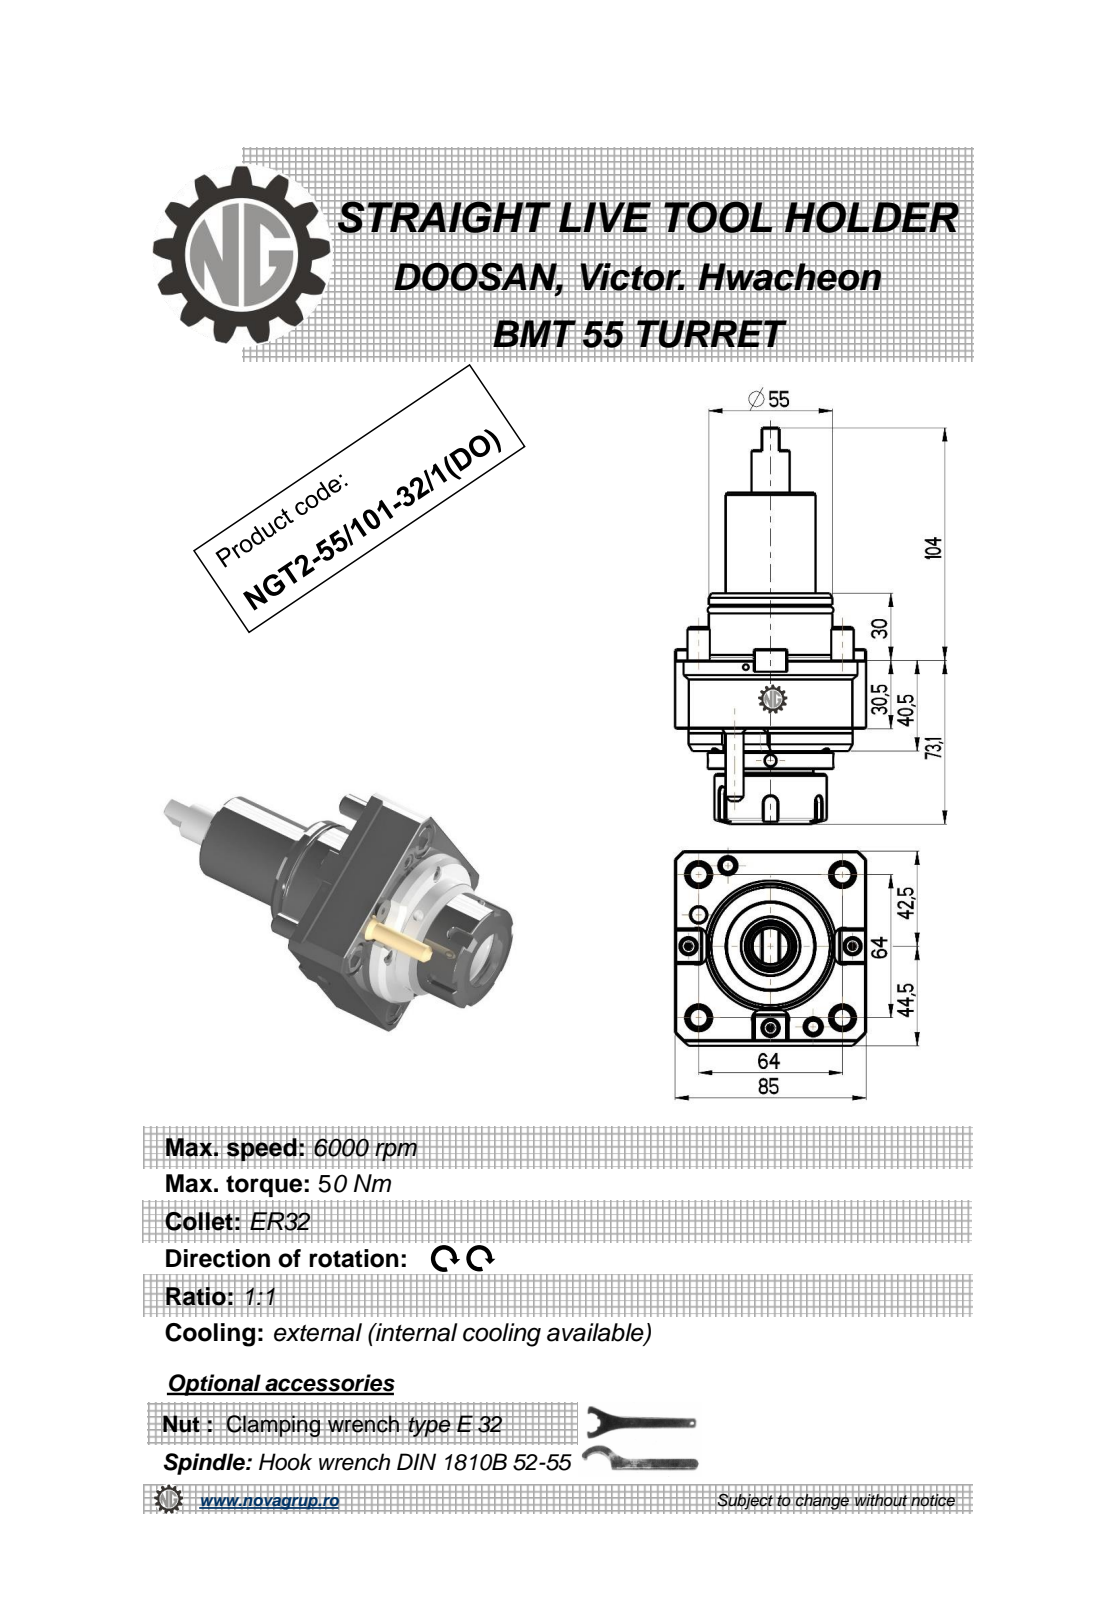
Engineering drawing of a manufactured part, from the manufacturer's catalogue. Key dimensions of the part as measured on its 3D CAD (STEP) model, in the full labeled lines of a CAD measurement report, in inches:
Part name (STEP PRODUCT): NGT2_55_101_32_1_DO
STEP written by: PRO/ENGINEER BY PARAMETRIC TECHNOLOGY CORPORATION, 2010280 (CONFIG_CONTROL_DESIGN)
Units: inches
Bodies: 2 solids, 304 faces (140 planar, 67 cylindrical, 97 other)
Overall size (bounding box): 6.972 × 3.425 × 3.346
Volume: 28.37 in³ · Surface area: 84.84 in²
Round holes (diameter × count): ⌀0.197 ×3, ⌀0.118 ×1, ⌀0.268 ×1, ⌀1.063 ×1
Round bosses / shafts (diameter × count): ⌀0.394 ×4, ⌀2.874 ×1, ⌀2.205 ×1, ⌀2.165 ×1, ⌀2.142 ×1, ⌀1.969 ×1, ⌀1.654 ×1, ⌀1.575 ×1
Partial cylindrical surfaces — rounded edges, fillets, slot ends (radius × count): R0.009 ×6, R0.118 ×5, R0.031 ×2, R0.236 ×2, R2.264 ×1
Main face-to-face distances: 1.201, 3.346, 0.394, 1.594, 3.425, 0.709, 0.791, 0.315, 0.413, 1.909
Hole centre spacings: 1.375, 1.461, 1.973
